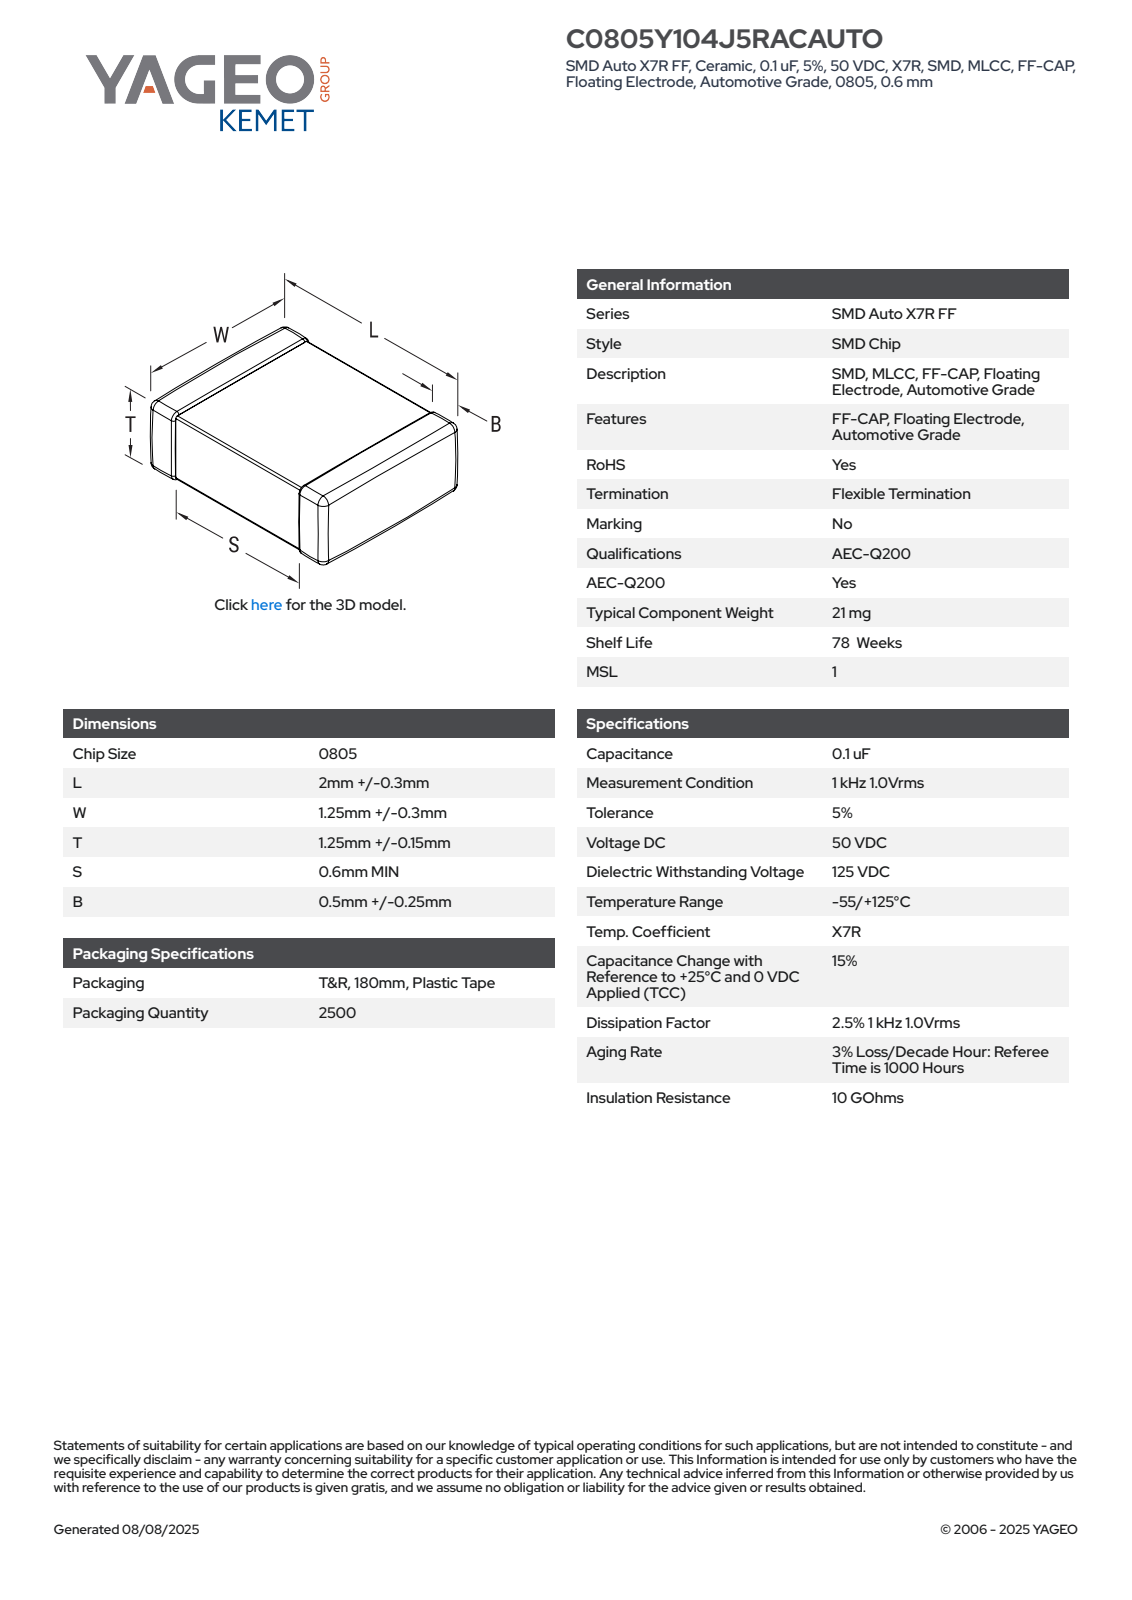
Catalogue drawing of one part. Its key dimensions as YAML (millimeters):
part_name: "CCS_CCSTD_0805_L2.3W1.55T1.4S0.6B0.75"
step_written_by: "SolidWorks 2021 (AUTOMOTIVE_DESIGN)"
units: millimeters
bodies: {solids: 4, faces: 121, planar: 71, cylindrical: 34, other: 16}
overall_size: [2.3, 1.55, 1.4]
volume: 5
surface_area: 18
face_to_face_distances: [1.37, 1.4, 1.52, 2.3, 1.55, 1.34, 1.49, 1.06, 1.24, 1.01]
